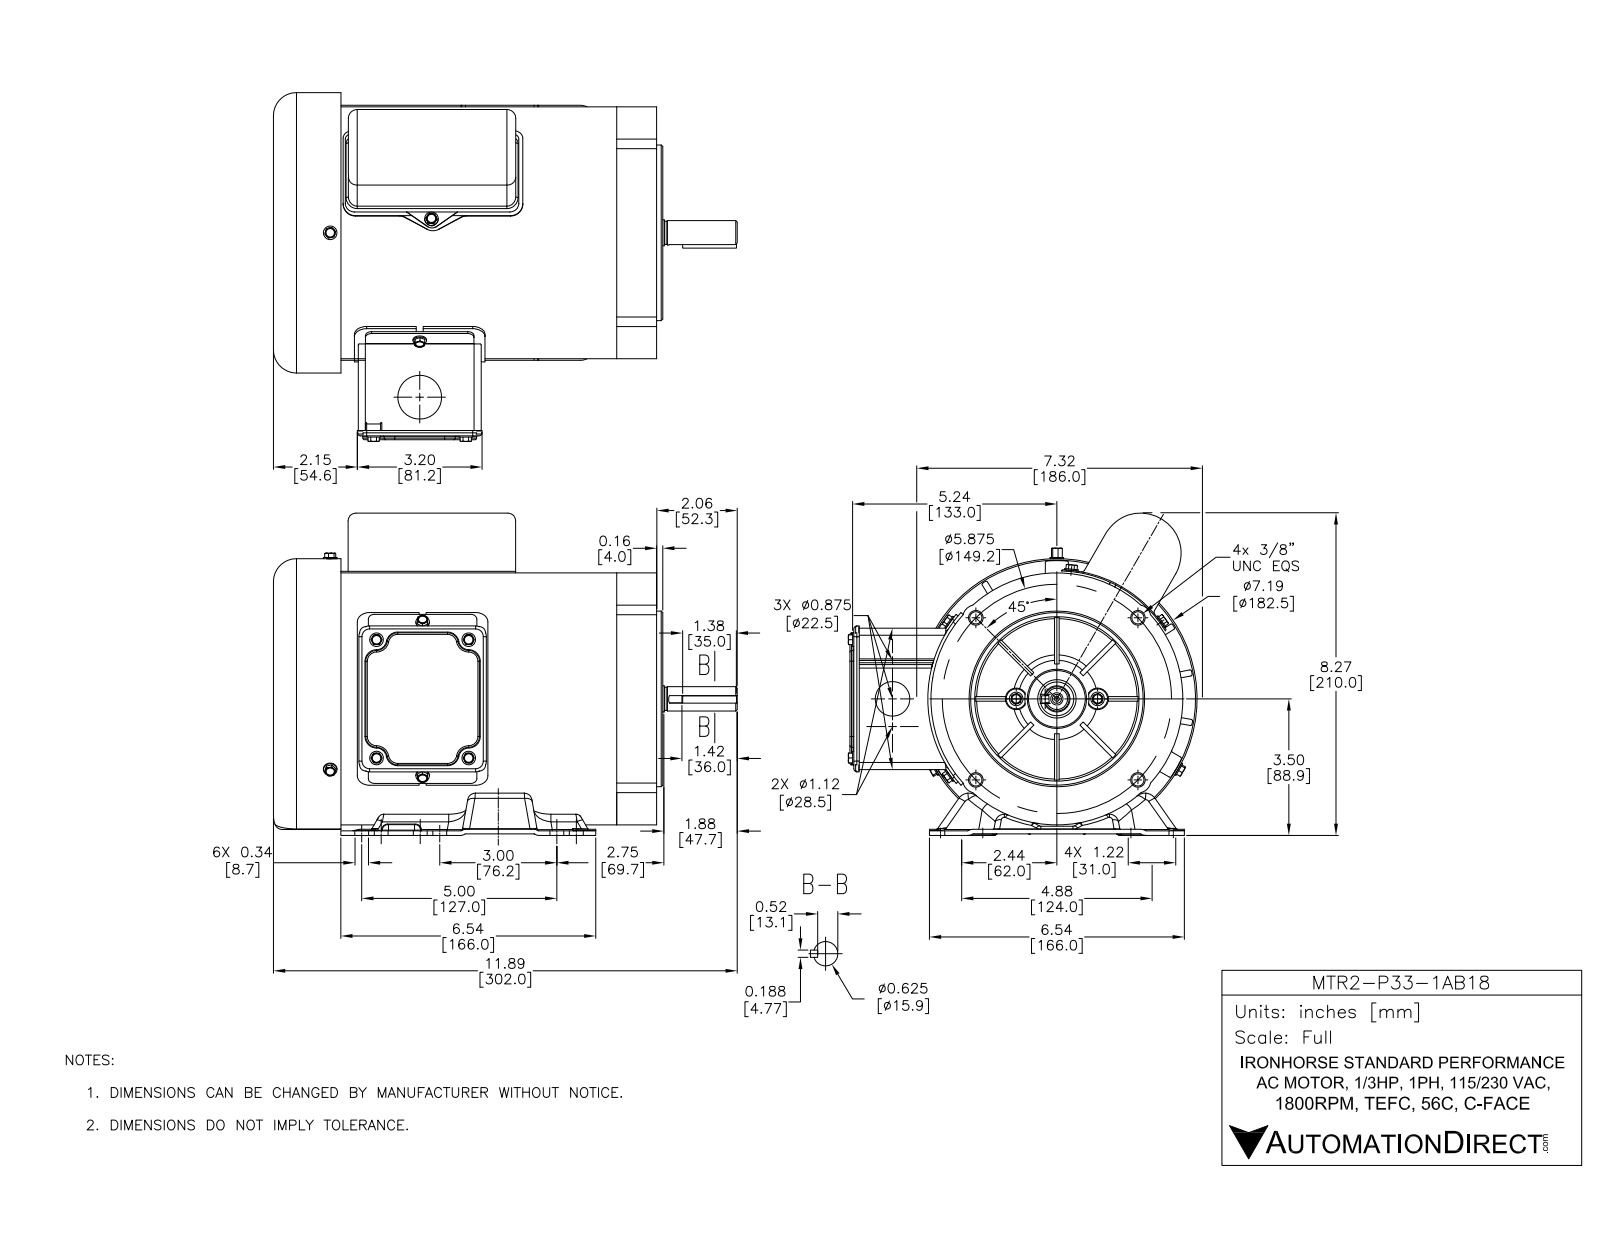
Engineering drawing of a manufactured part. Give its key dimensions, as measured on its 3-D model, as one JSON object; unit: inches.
{"part_name": "MTR2-P33-1AB18", "step_written_by": "SolidWorks 2016 (AUTOMOTIVE_DESIGN)", "units": "inches", "bodies": {"solids": 40, "faces": 2933, "planar": 827, "cylindrical": 938, "other": 1168}, "overall_size": [11.634, 8.938, 8.3], "volume_in3": 46.18, "surface_area_in2": 1045, "round_holes": [[0.197, 12], [0.219, 11], [0.276, 8], [0.217, 6], [0.344, 6], [0.136, 5], [0.15, 4], [0.177, 4], [0.313, 4], [0.709, 3], [0.13, 2], [0.134, 2]], "round_bosses_or_shafts": [[0.164, 11], [0.348, 7], [0.25, 6], [0.348, 4], [0.414, 2], [0.19, 2], [7.185, 1], [6.457, 1]], "partial_cylinders_radius": [[0.118, 125], [0.039, 38], [0.157, 32], [0.02, 30], [0.138, 26], [0.228, 20], [0.276, 19], [0.197, 17]], "face_to_face_distances": [0.118, 0.039, 0.063, 8.386, 1.024, 1.142, 9.567, 9.528, 0.047, 3.087], "hole_center_spacings": [4.221, 3.031, 0.094, 2.32, 2.409, 2.937, 2.979, 3.748]}
